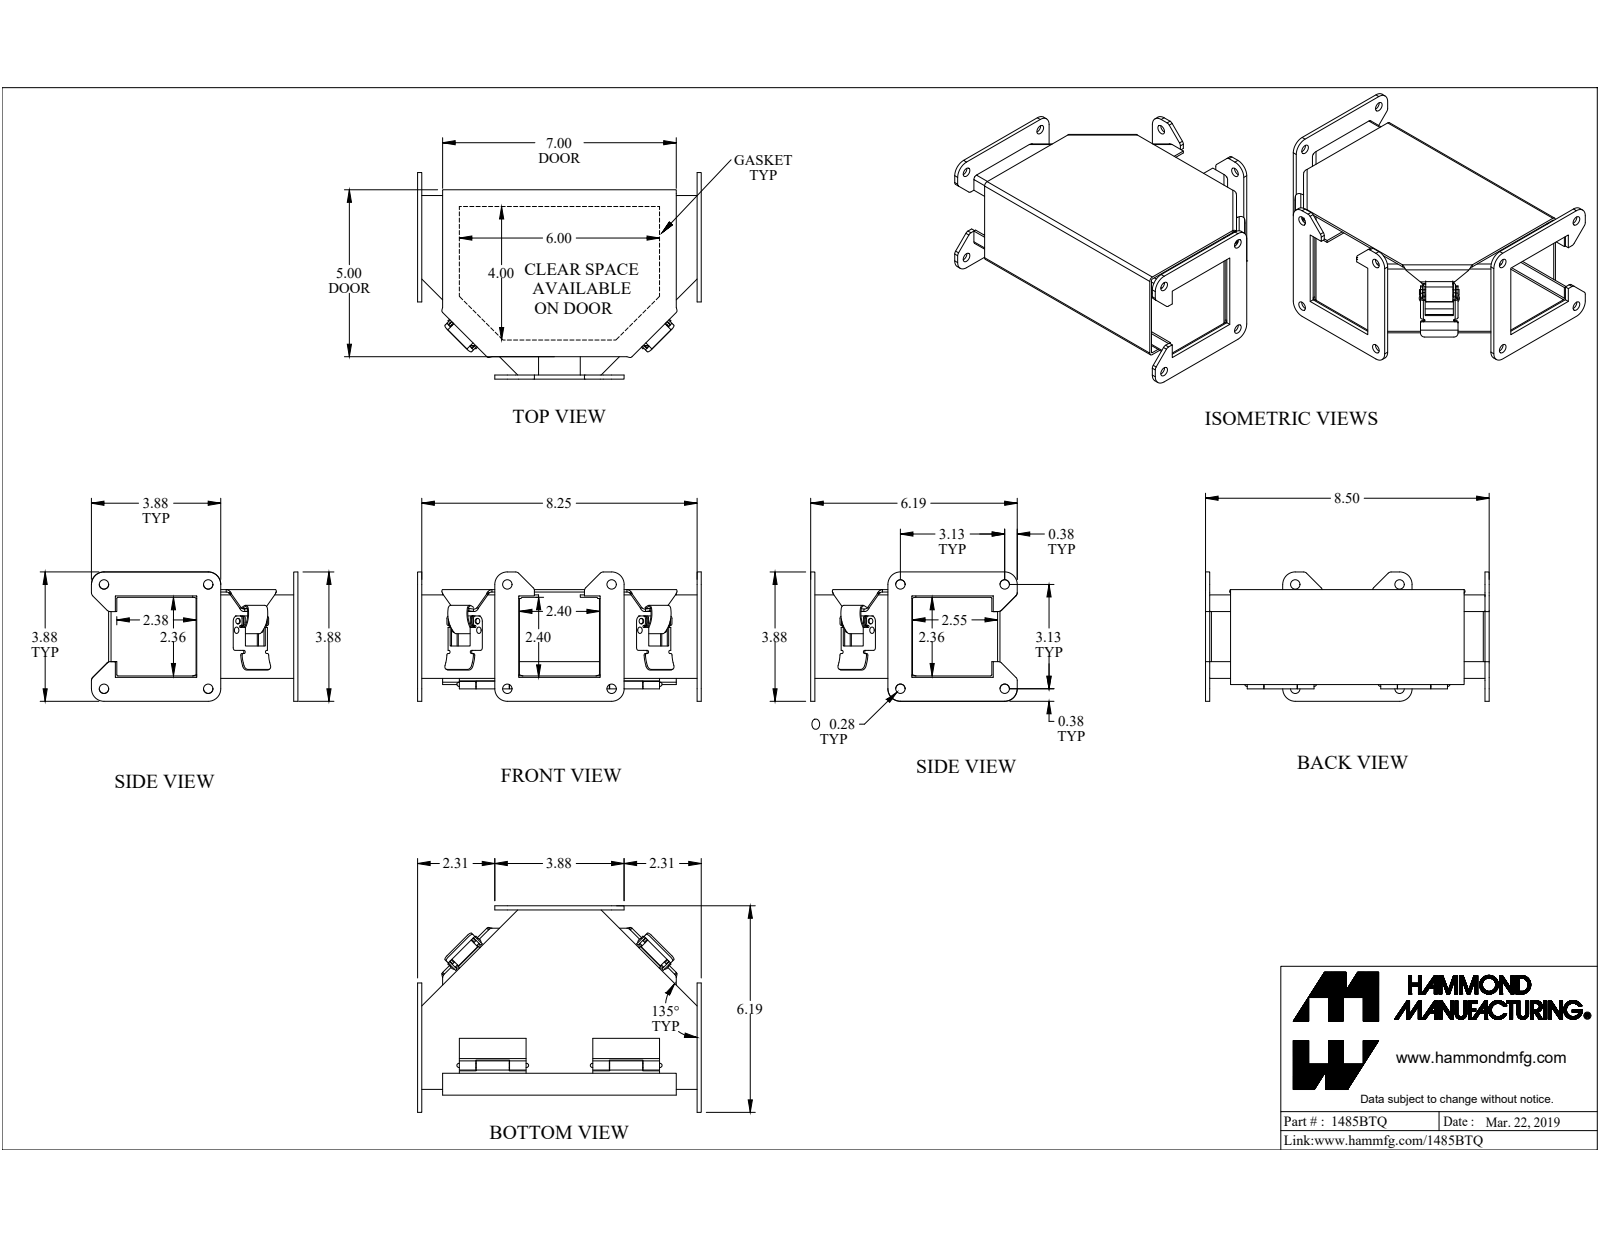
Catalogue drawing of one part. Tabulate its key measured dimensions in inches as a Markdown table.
| quantity | value |
| --- | --- |
| part name | 1485BTQ |
| STEP written by | SolidWorks 2019 (CONFIG_CONTROL_DESIGN) |
| units | inches |
| bodies | 17 solids, 464 faces (266 planar, 162 cylindrical, 36 other) |
| overall size | 8.5 × 6.188 × 3.876 |
| volume | 14.14 in³ |
| surface area | 384.3 in² |
| round holes (diameter × count) | 0.281 × 12, 0.164 × 4, 0.125 × 1 |
| round bosses / shafts (diameter × count) | 0.162 × 4, 0.158 × 4, 0.125 × 2, 0.275 × 1, 0.275 × 1, 0.125 × 1 |
| partial cylindrical surfaces (radius × count) | 0.125 × 18, 0.036 × 12, 0.108 × 12, 0.375 × 12, 0.029 × 8, 0.086 × 8, 0.078 × 6, 0.015 × 4 |
| main face-to-face distances | 0.072, 2.586, 0.158, 2.428, 2.658, 2.514, 2.5, 0.23, 2.356, 0.086 |
| hole center spacings | 3.125, 4.419, 2.099, 3.124, 3.125, 3.126, 4.418, 4.42 |
